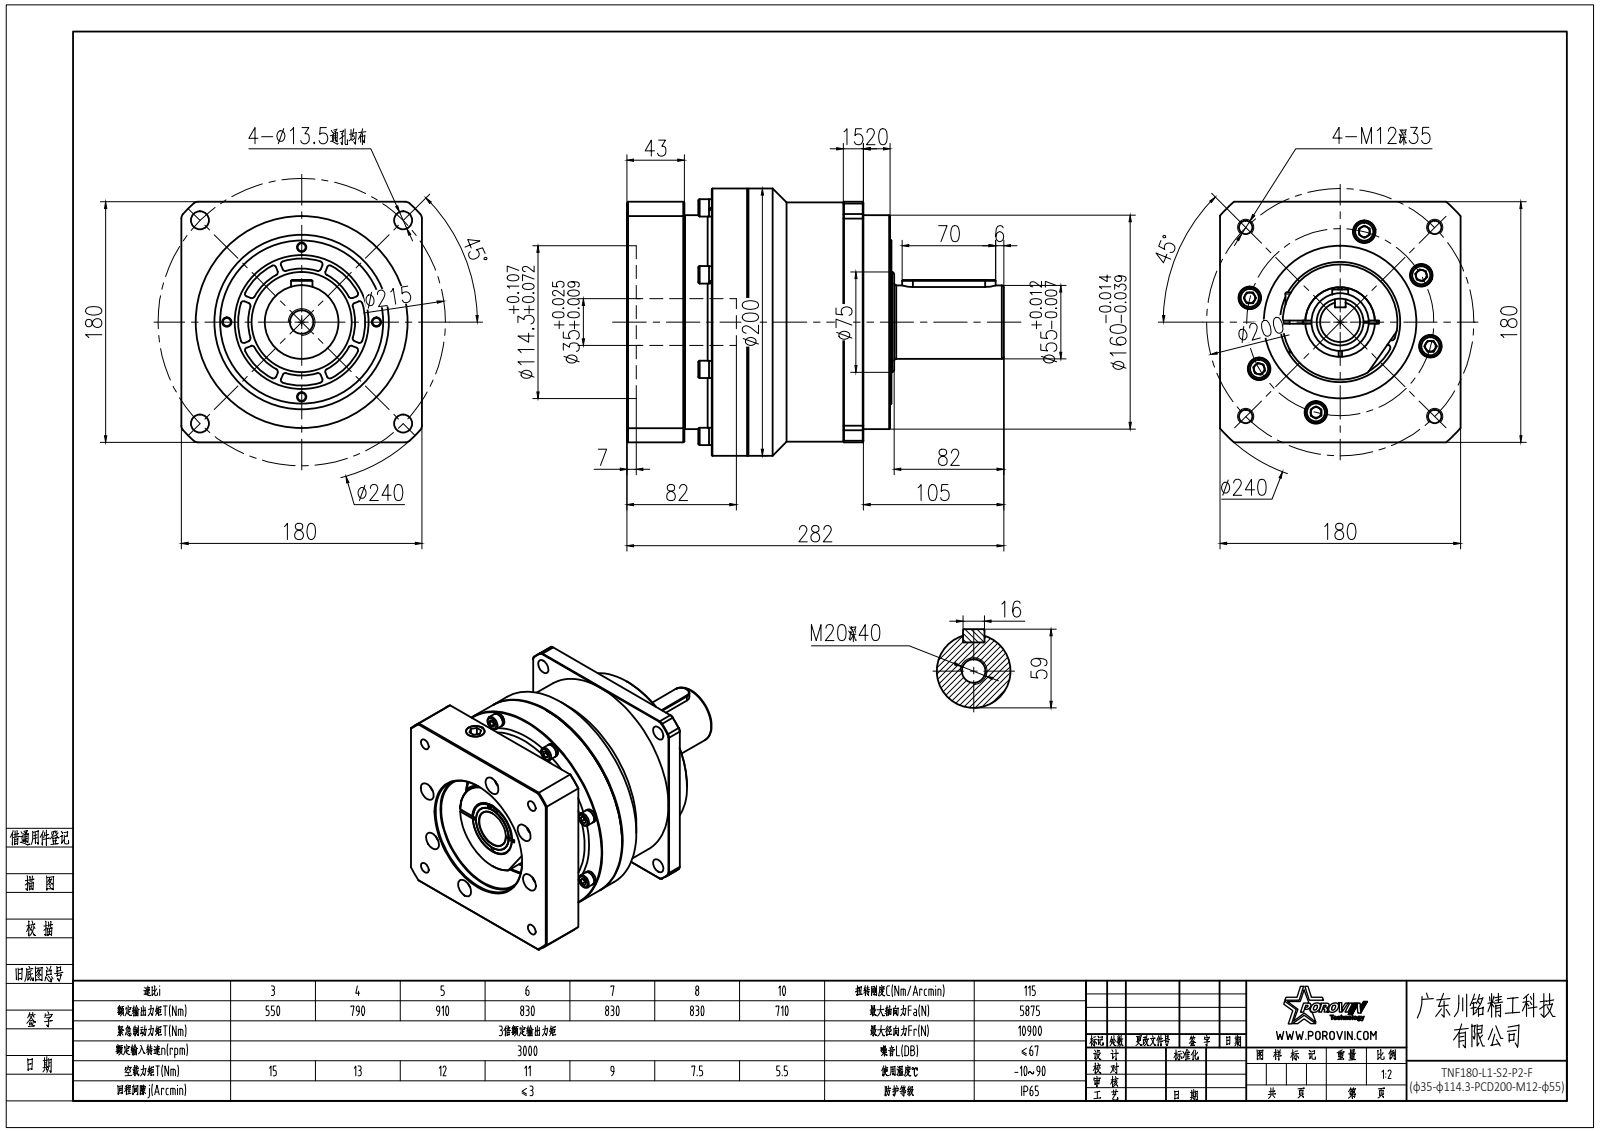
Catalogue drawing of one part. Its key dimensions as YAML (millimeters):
part_name: "KS180一级齿圈加出轴外形图; hex socket set screws with flat point gb_GB_FASTENER_SCREWS_HSFP M20X20-N; spring lock washers--normal type gb_GB_FASTENER_WASHER_SW 8; hexagon socket head cap screws gb_GB_FASTENER_SCREWS_HSHCS M8X35-N (+3 more)"
step_written_by: "SolidWorks 2016 (CONFIG_CONTROL_DESIGN)"
units: millimeters
bodies: {solids: 35, faces: 956, planar: 409, cylindrical: 346, other: 201}
overall_size: [282, 200, 200]
volume: 5085000
surface_area: 438920
round_holes:
  - {diameter: 8.68, count: 8}
  - {diameter: 9, count: 8}
  - {diameter: 8.5, count: 7}
  - {diameter: 11, count: 7}
  - {diameter: 10.9, count: 6}
  - {diameter: 17, count: 6}
  - {diameter: 6, count: 4}
  - {diameter: 10.2, count: 4}
  - {diameter: 13.5, count: 4}
  - {diameter: 17.5, count: 2}
  - {diameter: 20.5, count: 1}
  - {diameter: 35, count: 1}
round_bosses_or_shafts:
  - {diameter: 13, count: 8}
  - {diameter: 12.88, count: 8}
  - {diameter: 8, count: 8}
  - {diameter: 16, count: 7}
  - {diameter: 10, count: 7}
  - {diameter: 16.1, count: 6}
  - {diameter: 200, count: 1}
  - {diameter: 179, count: 1}
partial_cylinders:
  - {radius: 2, count: 32}
  - {radius: 8, count: 2}
  - {radius: 9, count: 1}
  - {radius: 10, count: 1}
  - {radius: 39, count: 1}
  - {radius: 48, count: 1}
  - {radius: 120, count: 1}
face_to_face_distances: [40.5, 50, 90.5, 180, 43, 2.5, 47.5, 177, 136.5, 23]
hole_center_spacings: [70, 139.99, 78.6, 92.5, 129.34, 130.81, 152.33, 1.26]
